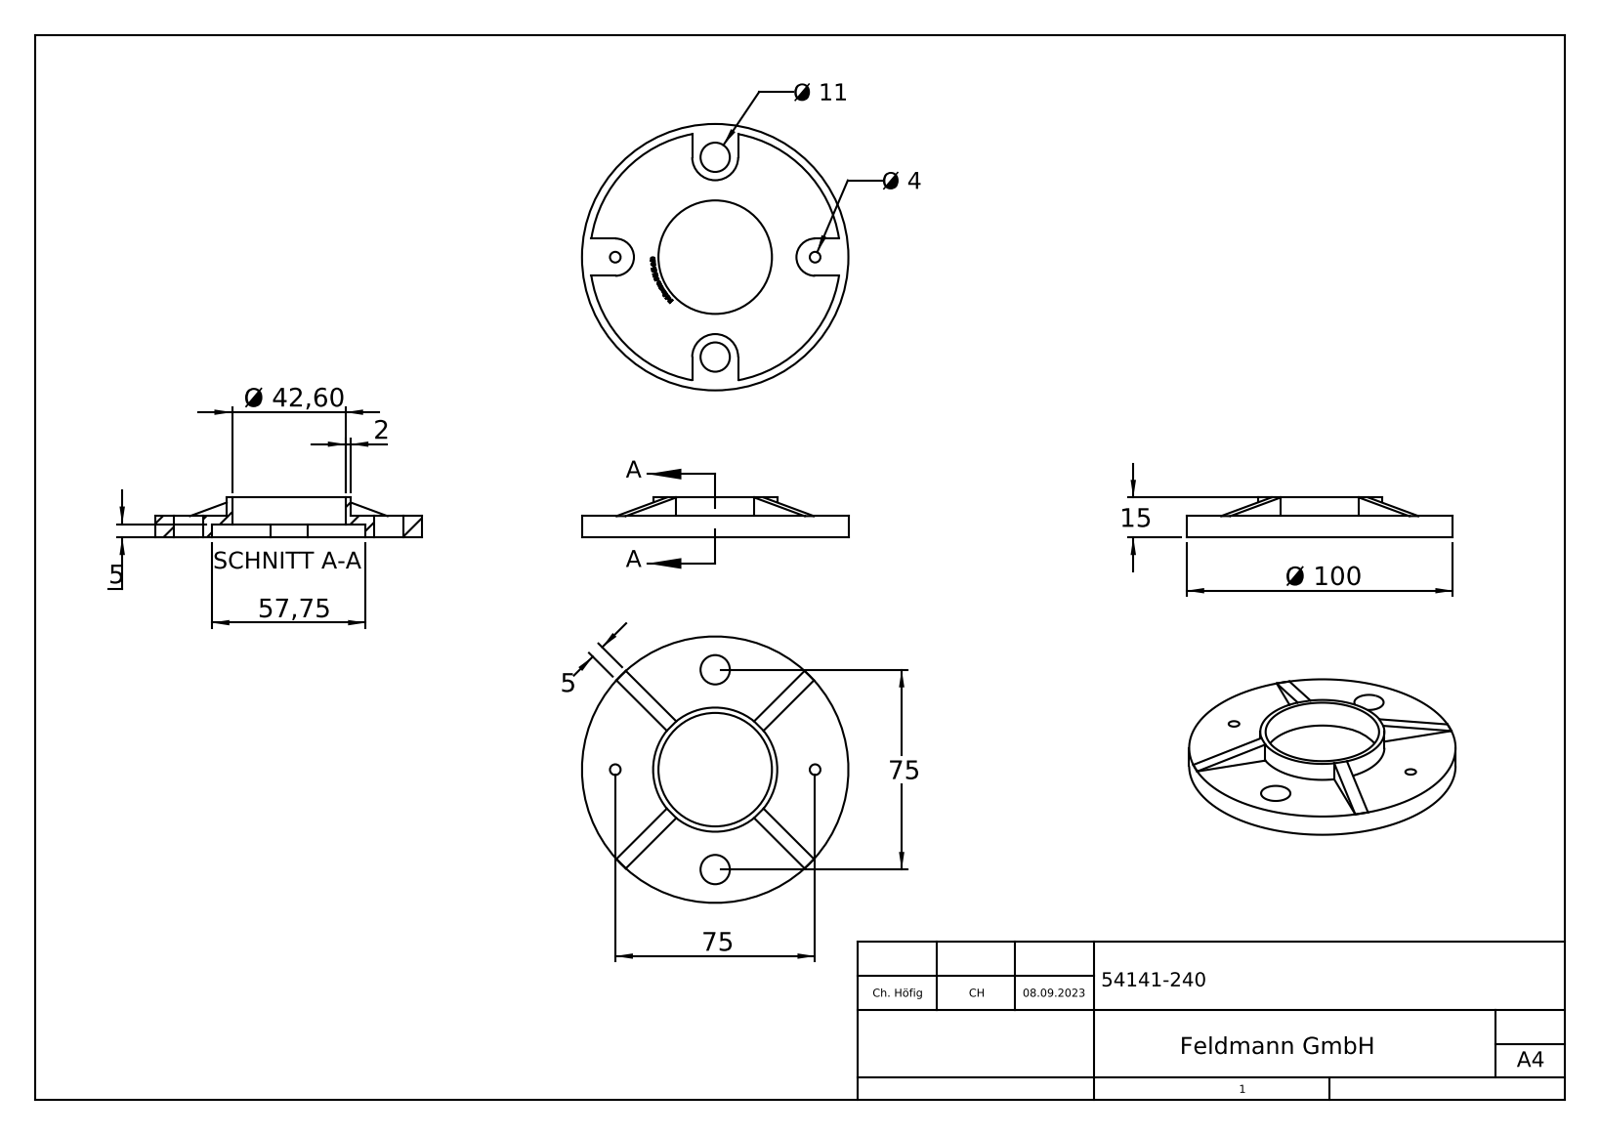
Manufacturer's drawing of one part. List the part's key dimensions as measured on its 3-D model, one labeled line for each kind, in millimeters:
Part name (STEP PRODUCT): 54141-240
STEP written by: SolidWorks 2018 (CONFIG_CONTROL_DESIGN)
Units: millimetres
Bodies: 1 solid, 265 faces (176 planar, 18 cylindrical, 71 other)
Overall size (bounding box): 100 × 100 × 15
Volume: 30 795 mm³ · Surface area: 20 701 mm²
Round holes (diameter × count): ⌀4 ×2, ⌀11 ×2, ⌀42.6 ×1
Round bosses / shafts (diameter × count): ⌀100 ×1, ⌀46.6 ×1
Partial cylindrical surfaces — rounded edges, fillets, slot ends (radius × count): R7 ×2, R8.62 ×2, R47 ×1
Main face-to-face distances: 3, 5, 8, 15, 10, 7, 14, 17.24, 5.1, 2.9
Hole centre spacings: 37.5, 53.03, 75
